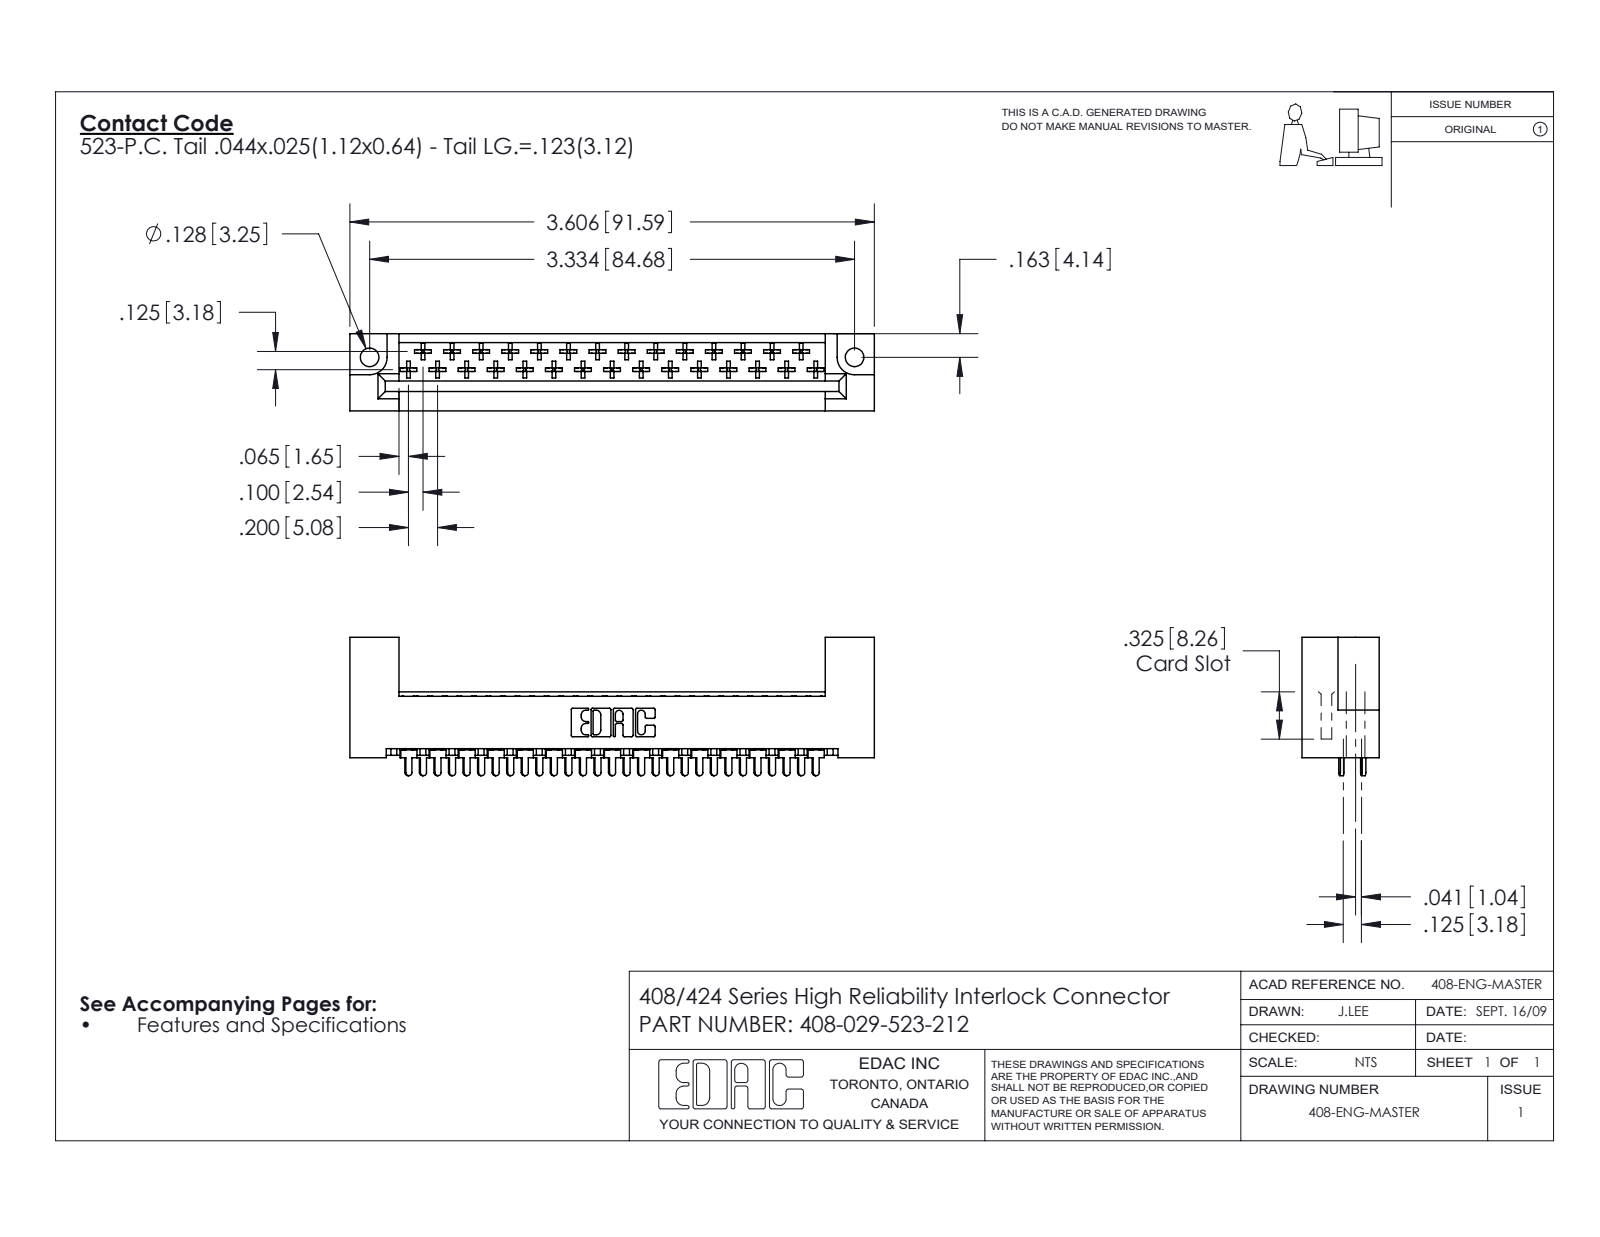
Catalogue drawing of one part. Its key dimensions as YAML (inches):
part_name: "408 Part_029 - 2; 408-290-001_408-290-123 - Top; 408-290-001_408-290-123 - Bottom; 408-029-523-212"
step_written_by: "SolidWorks 2016 (CONFIG_CONTROL_DESIGN)"
units: inches
bodies: {solids: 30, faces: 1737, planar: 1307, cylindrical: 314, other: 116}
overall_size: [3.606, 0.951, 0.531]
volume: 0.709
surface_area: 20.34
round_holes:
  - {diameter: 0.128, count: 2}
partial_cylinders:
  - {radius: 0.01, count: 174}
  - {radius: 0.02, count: 31}
  - {radius: 0.022, count: 29}
  - {radius: 0.01, count: 22}
  - {radius: 0.007, count: 6}
  - {radius: 0.031, count: 6}
  - {radius: 0.026, count: 3}
  - {radius: 0.12, count: 2}
face_to_face_distances: [0.531, 0.125, 0.1, 0.025, 0.025, 0.361, 0.398, 0.235, 0.259, 0.217]
hole_center_spacings: [3.334]
